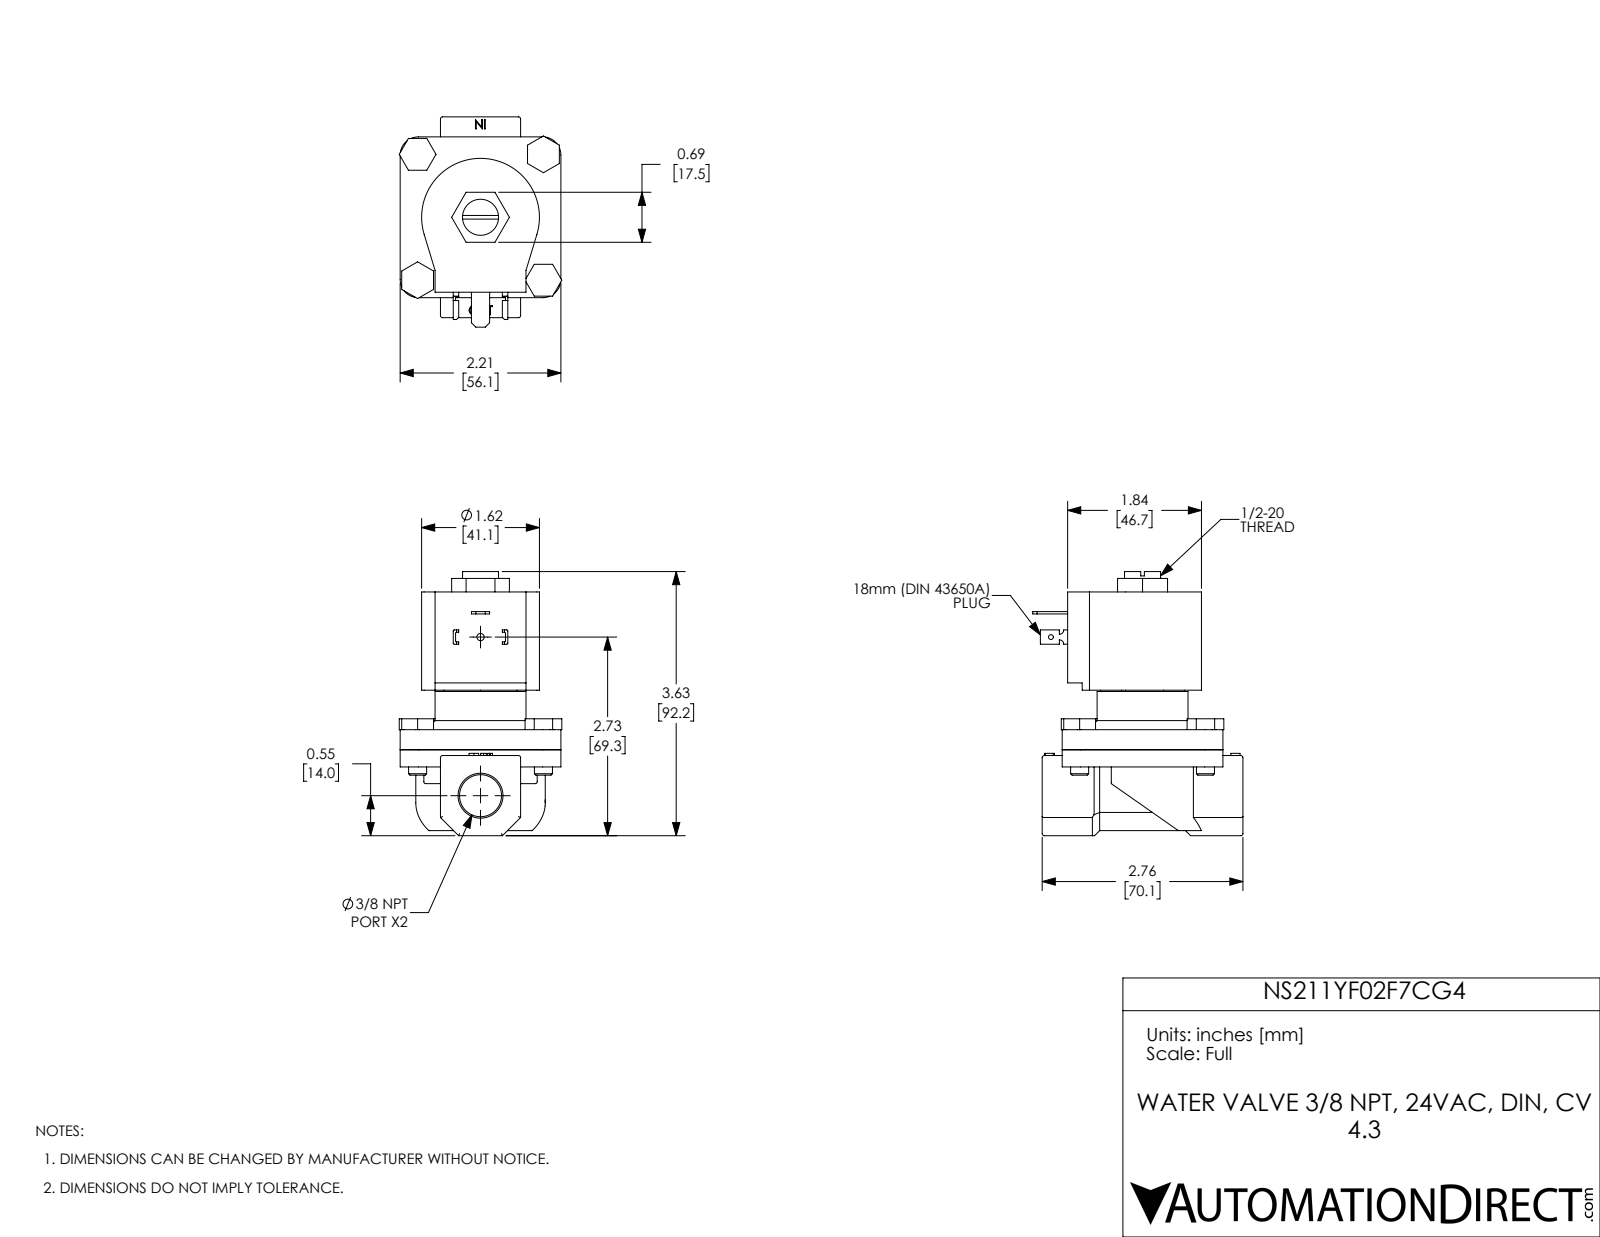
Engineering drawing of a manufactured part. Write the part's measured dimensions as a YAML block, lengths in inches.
part_name: "NS211YF02F7CG4"
step_written_by: "SolidWorks 2017 (AUTOMOTIVE_DESIGN)"
units: inches
bodies: {solids: 11, faces: 330, planar: 196, cylindrical: 99, other: 35}
overall_size: [3.63, 2.89, 2.235]
volume: 9.371
surface_area: 60.43
round_holes:
  - {diameter: 0.25, count: 4}
  - {diameter: 0.067, count: 1}
  - {diameter: 0.1, count: 1}
  - {diameter: 0.496, count: 1}
  - {diameter: 0.512, count: 1}
  - {diameter: 0.578, count: 1}
  - {diameter: 1.155, count: 1}
round_bosses_or_shafts:
  - {diameter: 0.248, count: 4}
  - {diameter: 1.25, count: 1}
partial_cylinders:
  - {radius: 0.03, count: 15}
  - {radius: 0.015, count: 8}
  - {radius: 0.25, count: 4}
  - {radius: 0.06, count: 2}
  - {radius: 0.81, count: 1}
  - {radius: 0.89, count: 1}
face_to_face_distances: [0.276, 2.169, 1.893, 0.554, 1.656, 0.236, 0.512, 2.405, 2.21, 1.102]
hole_center_spacings: [1.223, 1.73, 2.446, 2.18]
